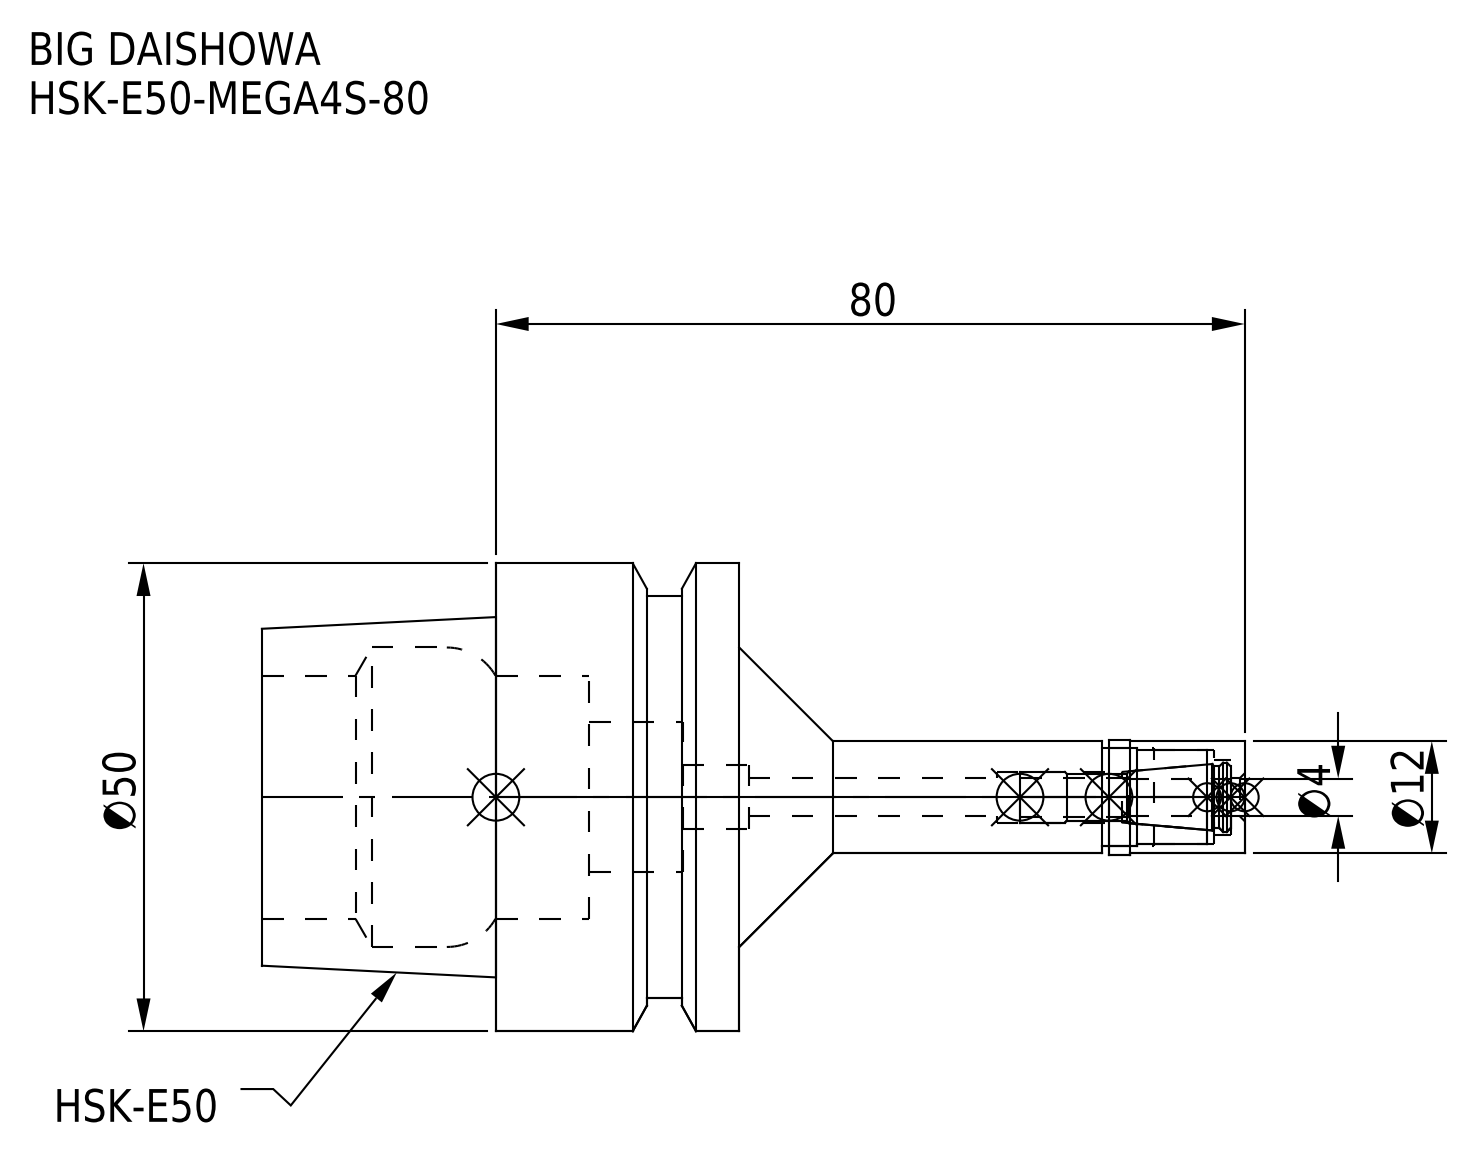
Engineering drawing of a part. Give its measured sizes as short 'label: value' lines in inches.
name: HSK-E50-MEGA4S-80-040.stp; HSK-E50-MEGA4S-80_1.stp; HSK-E50-MEGA4S-80-040-FreeParts; DXF_TEMP_ASSY_ASM_4_ASM.stp (+3 more)
written by: SolidWorks 2019 (CONFIG_CONTROL_DESIGN)
unit: in
bodies: 2 solids, 74 faces (18 planar, 40 cylindrical, 16 other)
size: 4.134 × 1.969 × 1.969
volume: 3.628 in³; area: 29.44 in²
holes: 1× ⌀0.161, 1× ⌀0.213, 1× ⌀0.268, 1× ⌀0.315, 1× ⌀0.394, 1× ⌀0.413, 1× ⌀0.63, 1× ⌀1.024, 1× ⌀1.26
bosses: 1× ⌀1.969, 1× ⌀1.693, 1× ⌀0.484, 1× ⌀0.472
face distances: 1.024, 0.984, 2.008, 0.632, 0.392, 1.376, 0.394, 0.238, 0.785, 1.77
